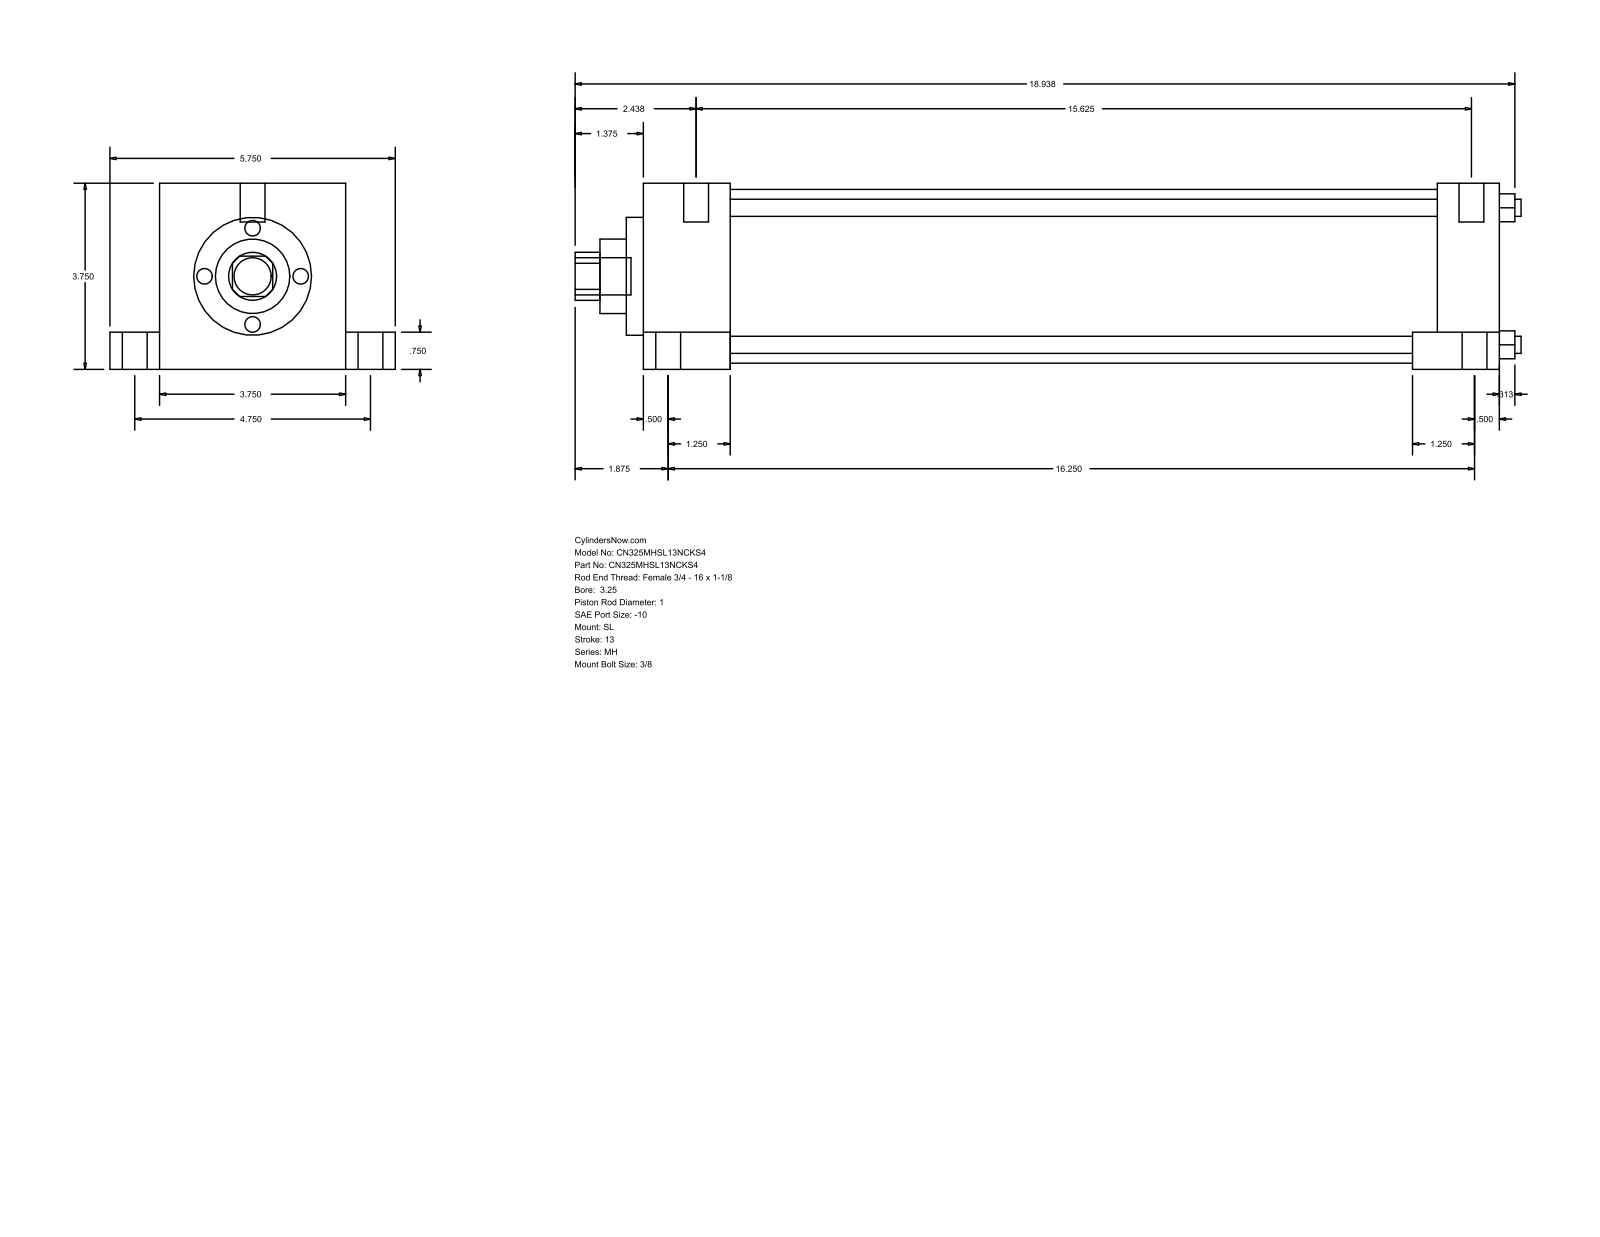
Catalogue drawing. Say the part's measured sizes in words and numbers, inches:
The part is named "MH_SL__0325_1". Its 3-D file was written by "GSSL Pune (CONFIG_CONTROL_DESIGN)". It is 0 solids with 110 faces: 77 planar, 33 cylindrical and 0 other. Overall it measures 19.063 by 5.75 by 3.75 inches. Round holes: 4 of diameter 0.345, 1 of diameter 1, 1 of diameter 1.5, 1 of diameter 2.375, 1 of diameter 3.5. Round bosses or shafts: 6 of diameter 0.5, 5 of diameter 0.75, 4 of diameter 0.219. Partial cylindrical surfaces (rounded edges, fillets, slot ends): 1 of radius 0.484. The main face-to-face distances are 3.75, 17.25, 1.75, 15.5, 1, 4.75, 0.75, 3, 16, 14.25. The hole center spacings are 1.952, 2.76, 3.903.
